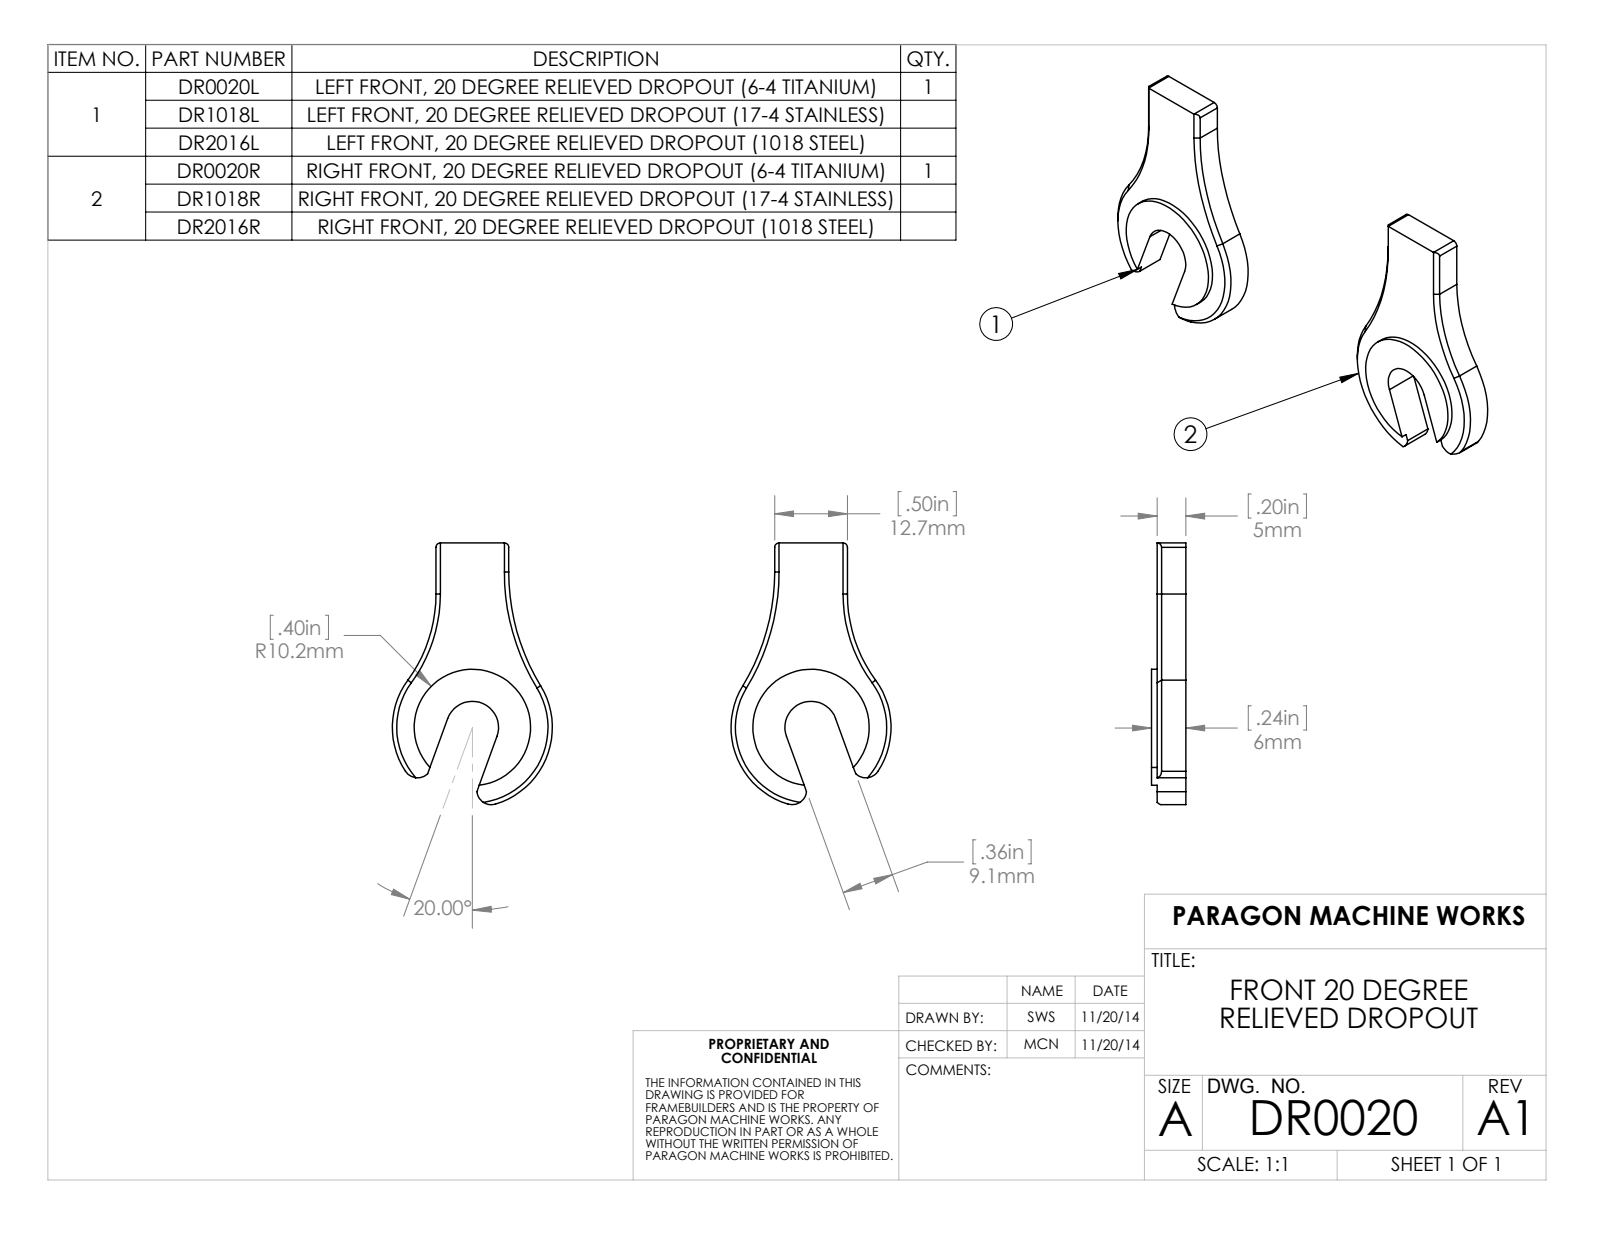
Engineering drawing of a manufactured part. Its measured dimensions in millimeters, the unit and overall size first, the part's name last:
Units: millimetres
Overall size (bounding box): 87.08 × 45.68 × 6
Round bosses / shafts (diameter × count): ⌀20.32 ×2
Partial cylindrical surfaces — rounded edges, fillets, slot ends (radius × count): R0.76 ×4, R2.54 ×4, R4.57 ×2, R13.97 ×2, R25.4 ×2, R38.1 ×2
Main face-to-face distances: 5, 1, 6, 9.15, 12.7, 59.14, 71.84, 46.44, 41.81
Volume: 7 505 mm³ · Surface area: 4 442 mm²
Bodies: 2 solids, 52 faces (20 planar, 24 cylindrical, 8 other)
Part name (STEP PRODUCT): DR0020R; DR0020L; DR0020
STEP written by: SolidWorks 2014 (AUTOMOTIVE_DESIGN)
